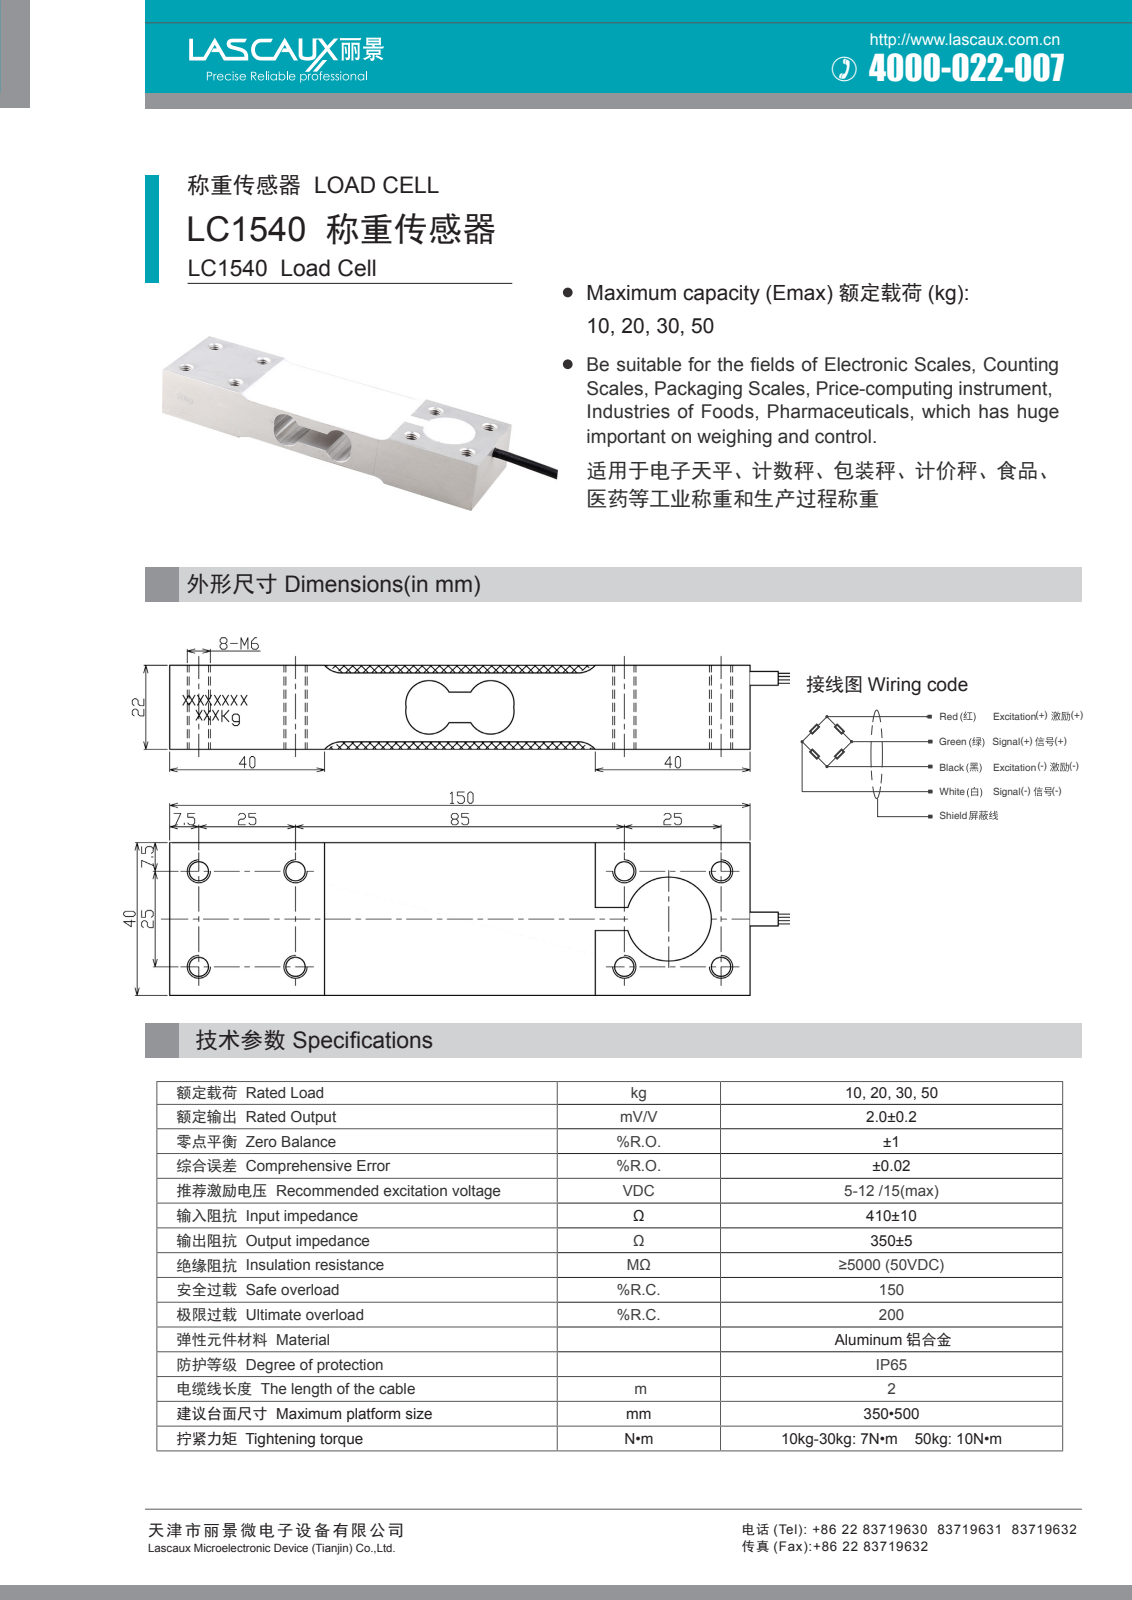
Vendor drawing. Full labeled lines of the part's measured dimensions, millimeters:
Part name (STEP PRODUCT): 传感器LC1540
STEP written by: SolidWorks 2016 (CONFIG_CONTROL_DESIGN)
Units: millimetres
Bodies: 1 solid, 45 faces (17 planar, 28 cylindrical, 0 other)
Overall size (bounding box): 160 × 40 × 22
Volume: 103 488 mm³ · Surface area: 25 642 mm²
Round holes (diameter × count): ⌀5 ×8
Round bosses / shafts (diameter × count): ⌀4 ×1
Partial cylindrical surfaces — rounded edges, fillets, slot ends (radius × count): R1 ×4, R5 ×4
Main face-to-face distances: 2, 20, 22, 40, 18, 7, 15, 5, 13, 150
Hole centre spacings: 25, 35.36, 110, 112.81, 85, 88.6, 135, 137.3
